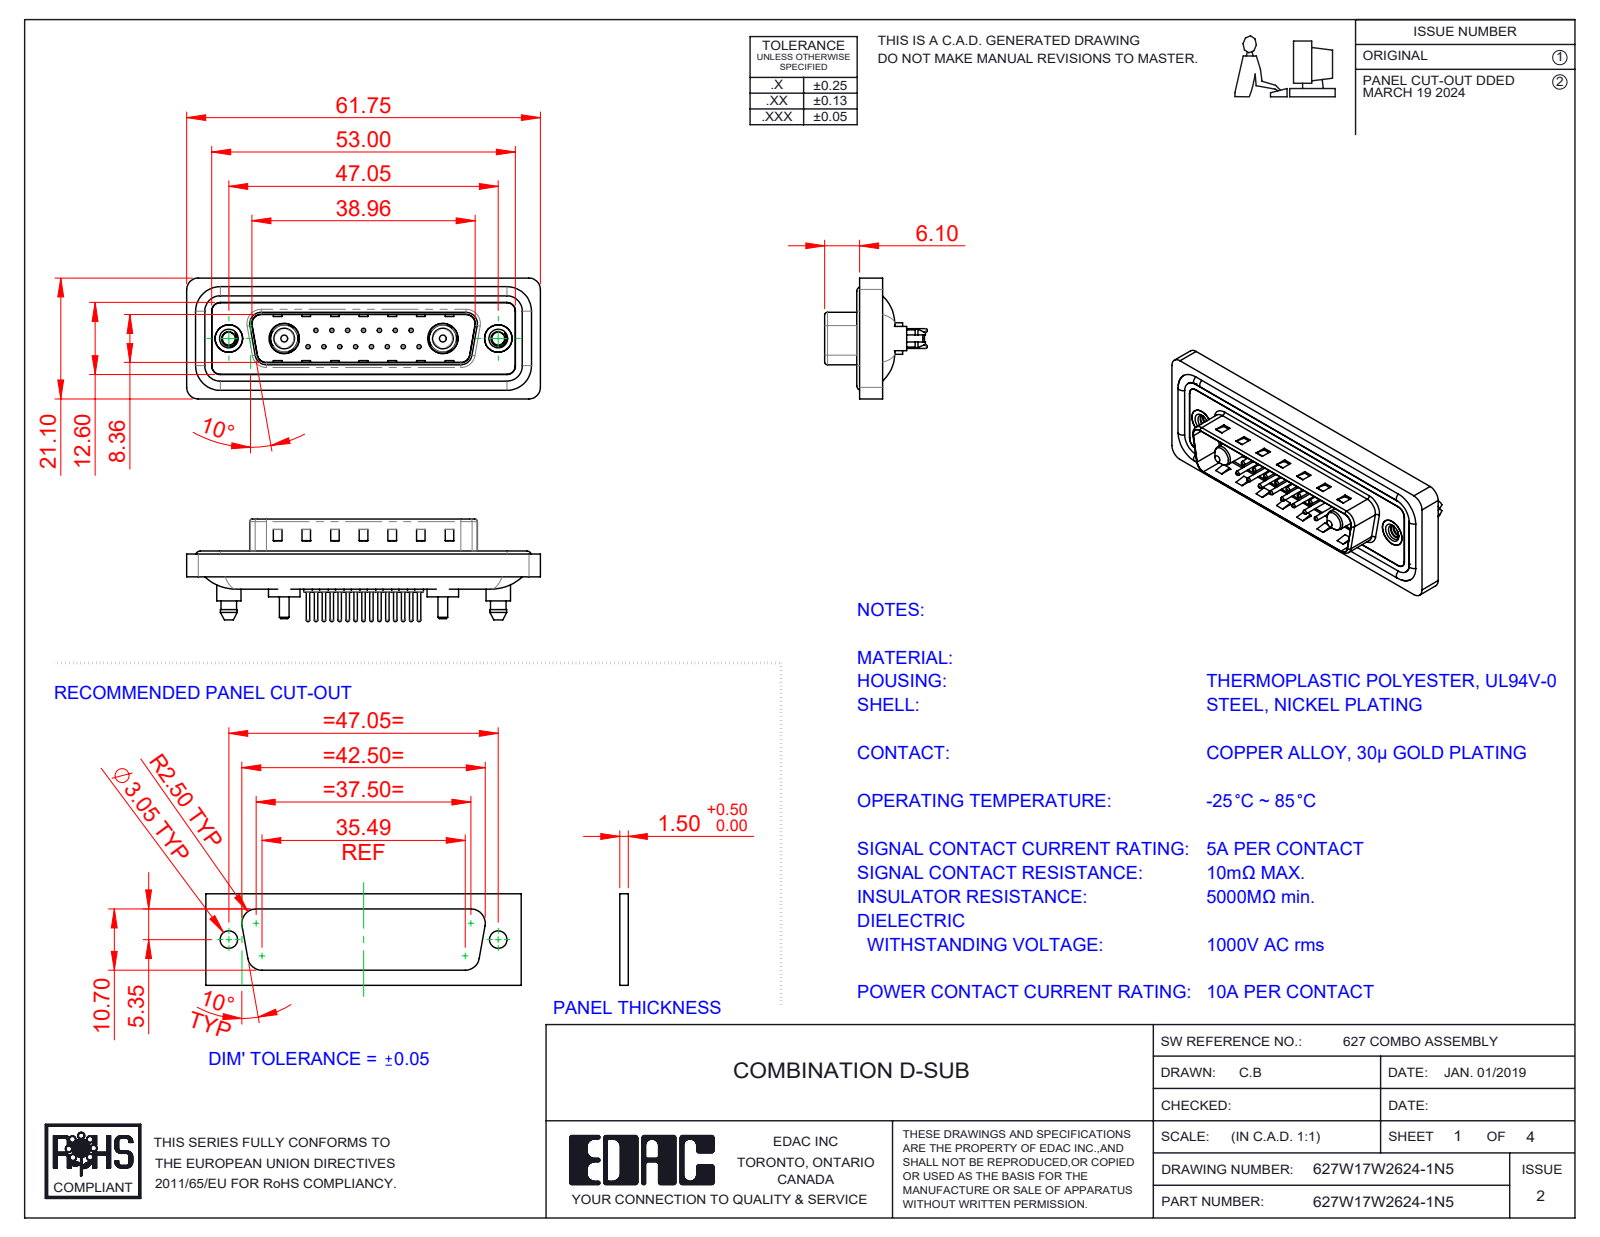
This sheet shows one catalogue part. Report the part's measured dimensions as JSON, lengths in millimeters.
{"part_name": "627Combo Shell Rear_25 Contacts; Power Pin_10A S; 627Combo Shell Front_25 Contacts; 627Combo Waterproof Housing_25 Contacts (+5 more)", "step_written_by": "SolidWorks 2023 (CONFIG_CONTROL_DESIGN)", "units": "millimeters", "bodies": {"solids": 26, "faces": 1166, "planar": 350, "cylindrical": 468, "other": 348}, "overall_size": [61.75, 21.1, 17.9], "volume_mm3": 7371, "surface_area_mm2": 12222, "round_holes": [[0.75, 15], [1.6, 15], [2, 15], [2.26, 2], [4, 2], [4.8, 2], [4.85, 2], [5, 2], [5.3, 2]], "round_bosses_or_shafts": [[1.5, 15], [0.6, 15], [1.6, 4], [5.5, 2], [5.4, 2], [5.2, 2], [4.9, 2], [4.75, 2]], "partial_cylinders_radius": [[1.5, 24], [2, 18], [1.6, 10], [0.5, 8], [0.25, 4], [0.6, 4], [0.65, 4], [0.9, 4]], "face_to_face_distances": [0.4, 1.5, 1.1, 1.6, 0.5, 3.1, 2.9, 0.82, 9.58, 4.1], "hole_center_spacings": [3.16, 2.77, 5.54, 8.31, 5.04, 7.49, 11.08, 5.03]}
